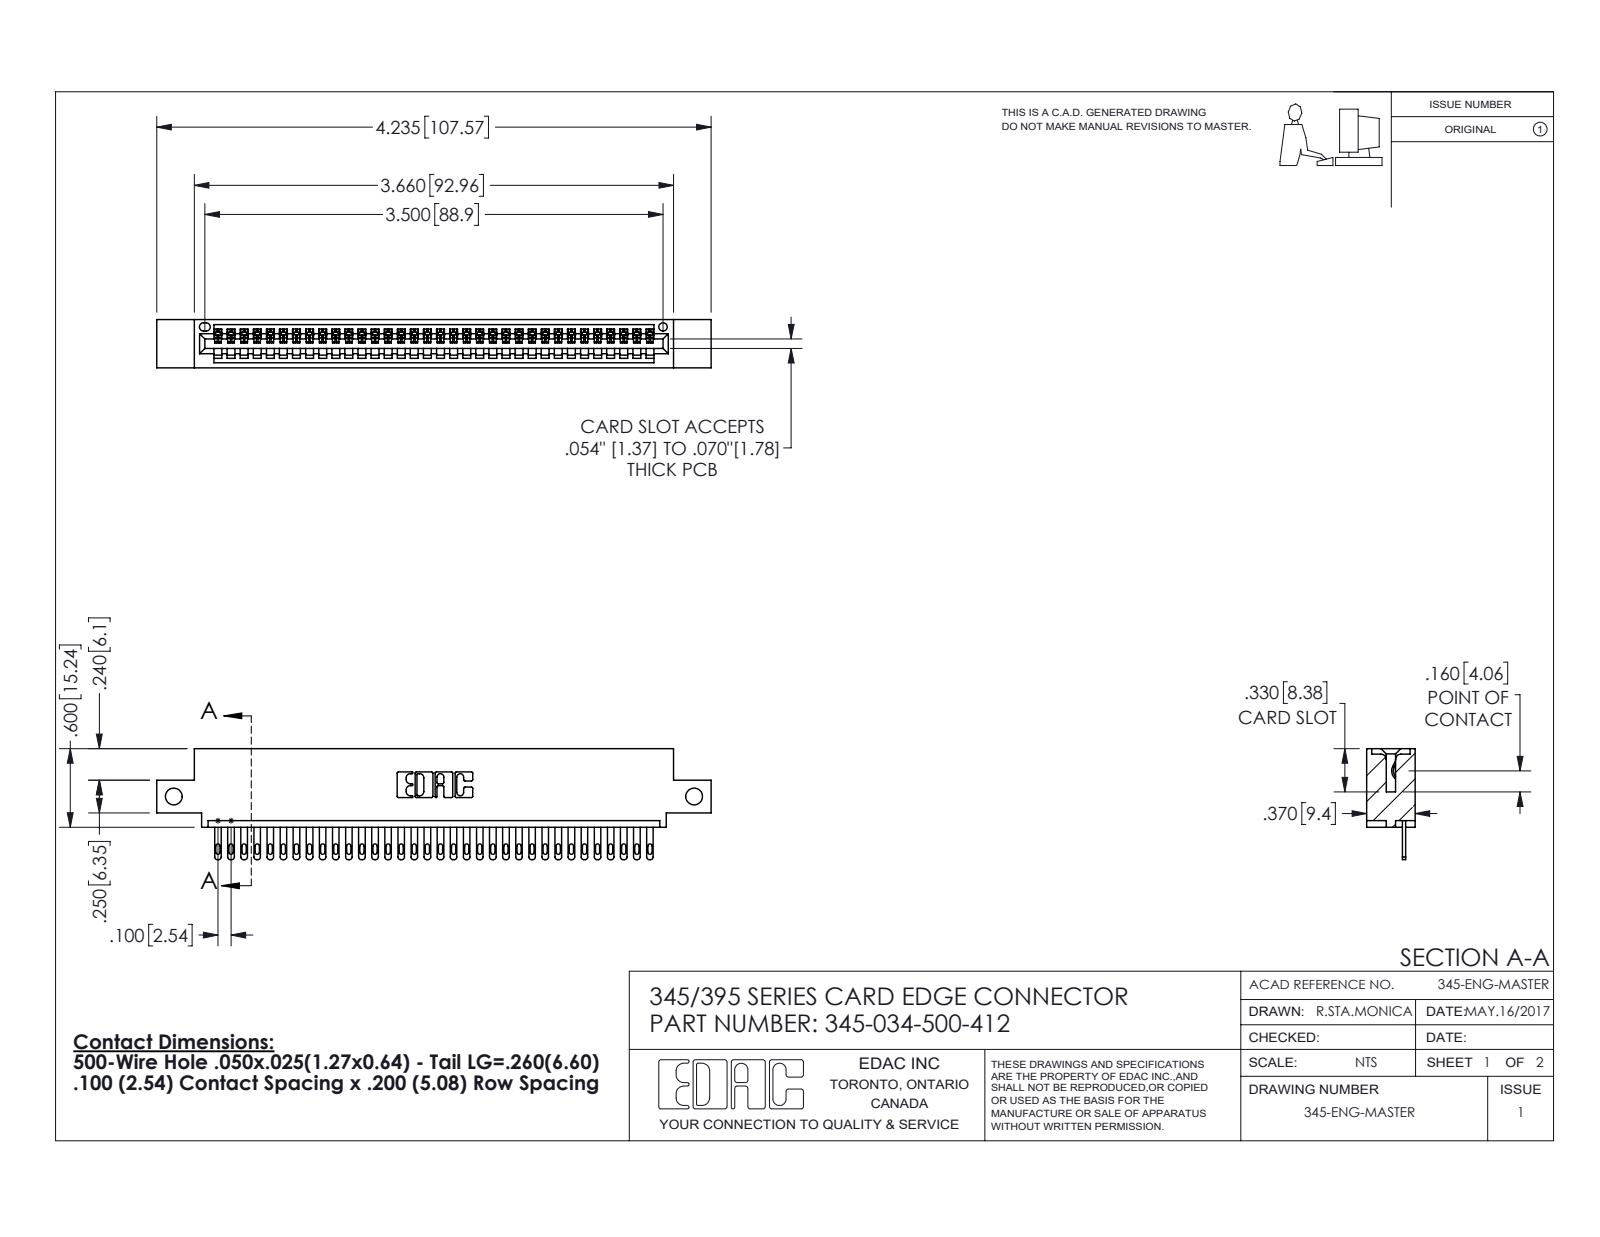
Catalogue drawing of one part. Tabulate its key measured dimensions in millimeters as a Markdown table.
| quantity | value |
| --- | --- |
| part name | 345-034-500-412; 345-292-001_345-293-100; 345 Part_0.110 Offset - Side Mount |
| STEP written by | SolidWorks 2016 (CONFIG_CONTROL_DESIGN) |
| units | millimeters |
| bodies | 35 solids, 1966 faces (1240 planar, 726 cylindrical, 0 other) |
| overall size | 107.6 × 21.5 × 9.4 |
| volume | 10 000 mm³ |
| surface area | 13 210 mm² |
| round holes (diameter × count) | 3.3 × 2, 1.6 × 1 |
| partial cylindrical surfaces (radius × count) | 0.2 × 68, 0.4 × 68, 0.5 × 68, 0.3 × 22, 0.2 × 6, 0.8 × 6, 0.7 × 3, 0.8 × 2 |
| main face-to-face distances | 1.8, 7.6, 9.4, 5.1, 2.5, 6.9, 0.6, 5.7, 3.8, 1.8 |
| hole center spacings | 101 |
